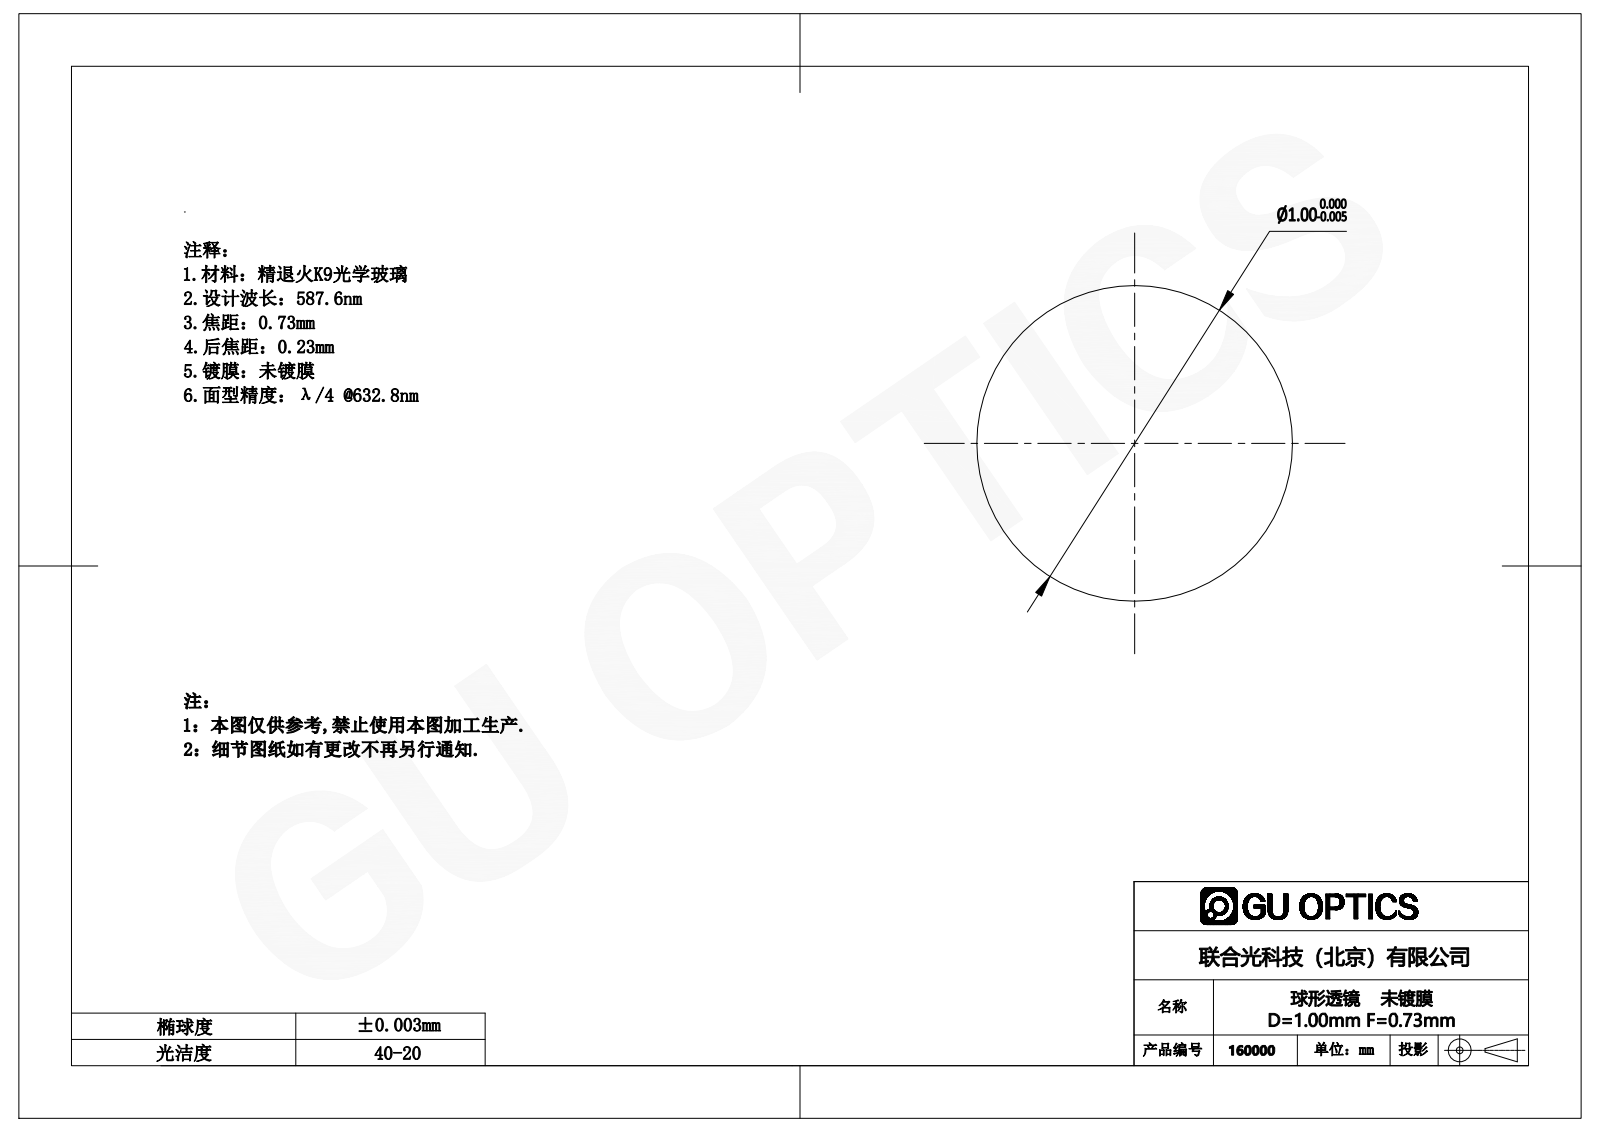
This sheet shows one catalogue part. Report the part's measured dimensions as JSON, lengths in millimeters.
{"part_name": "球形透镜", "step_written_by": "SolidWorks 2016 (CONFIG_CONTROL_DESIGN)", "units": "millimeters", "bodies": {"solids": 1, "faces": 2, "planar": 0, "cylindrical": 0, "other": 2}, "overall_size": [1, 1, 1], "volume_mm3": 0.524, "surface_area_mm2": 3}
